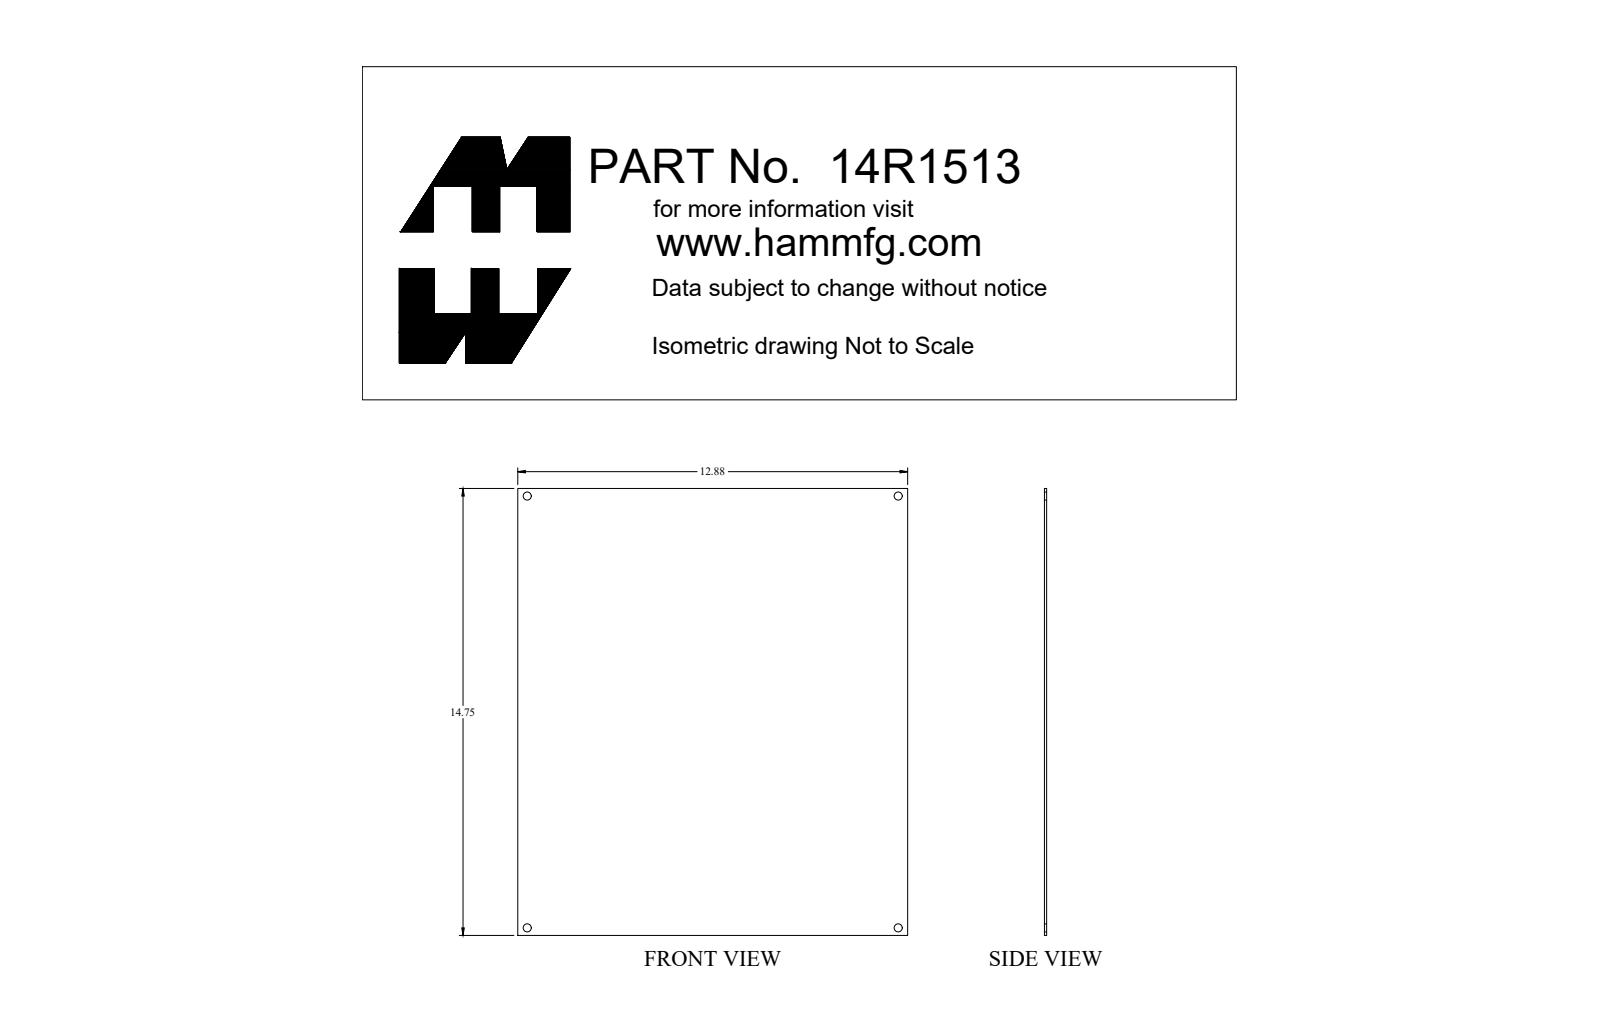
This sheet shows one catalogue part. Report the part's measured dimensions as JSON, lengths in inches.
{"part_name": "14R1513", "step_written_by": "SolidWorks 2018 (AUTOMOTIVE_DESIGN)", "units": "inches", "bodies": {"solids": 1, "faces": 10, "planar": 6, "cylindrical": 4, "other": 0}, "overall_size": [14.75, 12.875, 0.072], "volume_in3": 13.66, "surface_area_in2": 383.6, "round_holes": [[0.265, 4]], "face_to_face_distances": [0.072, 12.875, 14.75], "hole_center_spacings": [12.25, 14.25, 18.791]}
